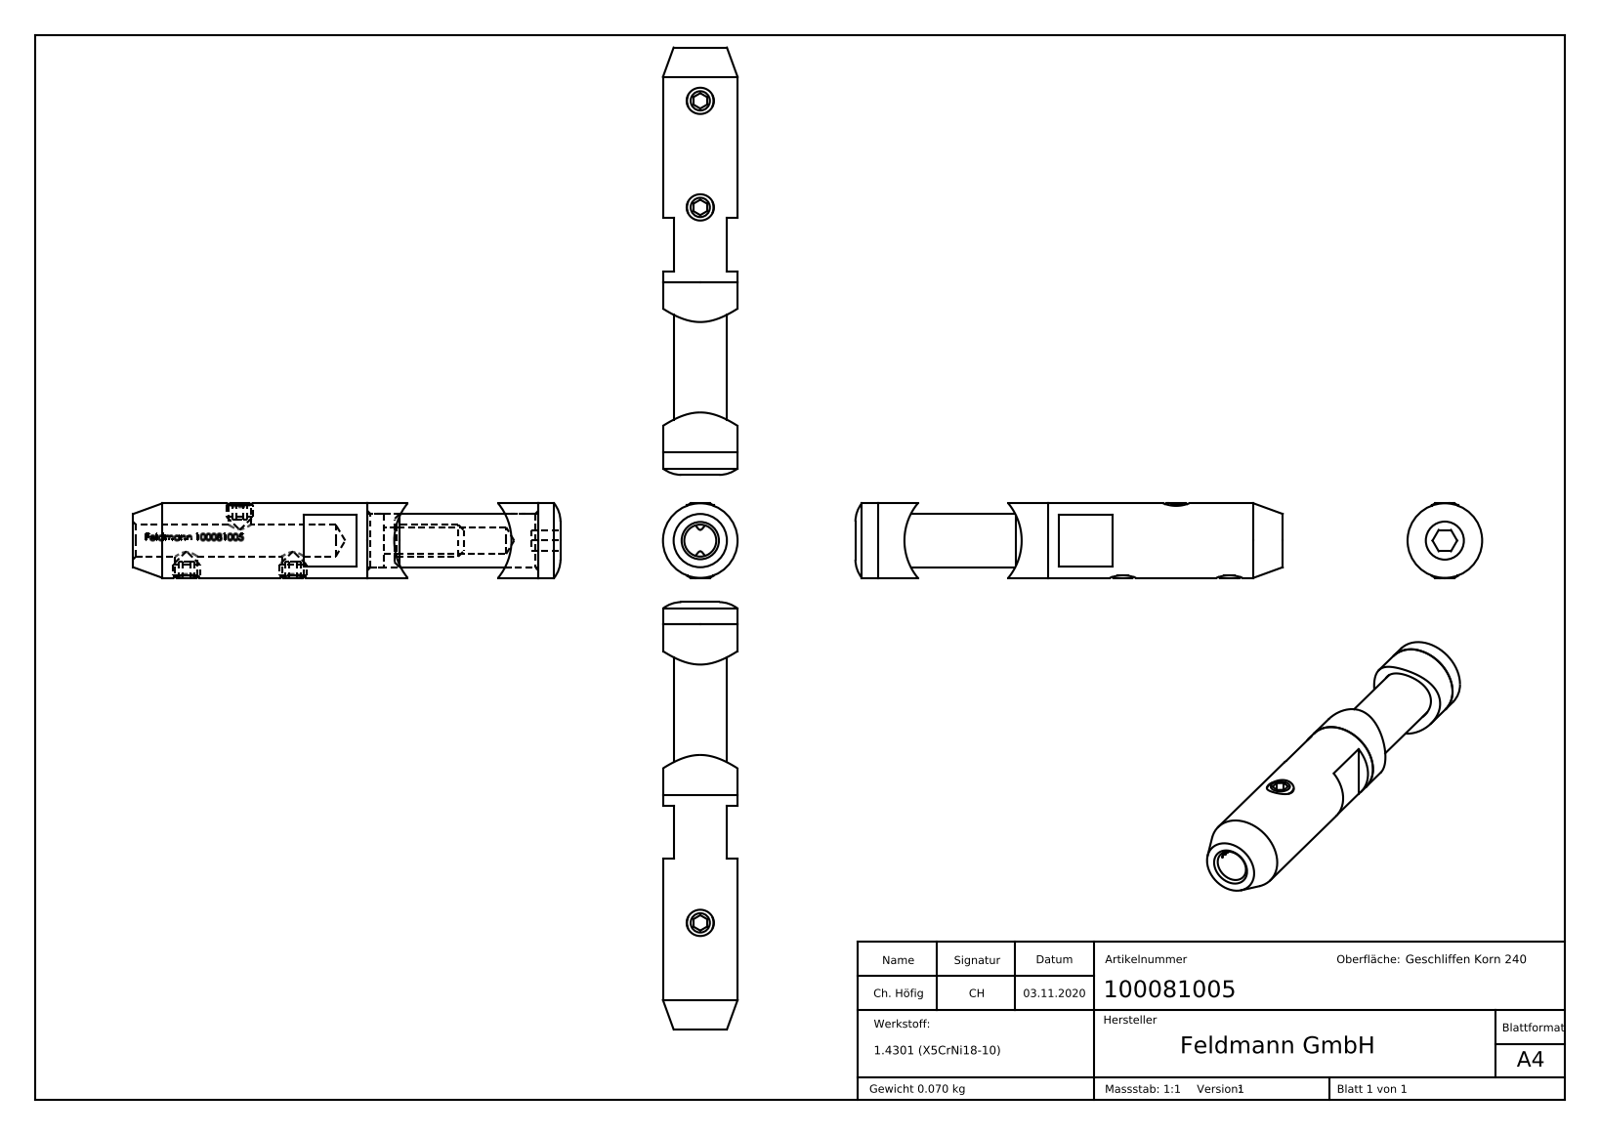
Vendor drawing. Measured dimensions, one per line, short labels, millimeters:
name: 10008100X Teil3; DIN 914 M5x6; DIN 914 M5x6_DIN914 M5x5; 100081005 (+5 more)
written by: SolidWorks 2018 (CONFIG_CONTROL_DESIGN)
unit: mm
bodies: 7 solids, 346 faces (119 planar, 71 cylindrical, 156 other)
size: 80.2 × 14 × 14
volume: 8 853 mm³; area: 6 552 mm²
holes: 3× ⌀4.2, 1× ⌀5, 1× ⌀6, 1× ⌀10.1
bosses: 3× ⌀5, 1× ⌀14, 1× ⌀10
rounds: 1× R3.1, 1× R11
face distances: 32, 10, 3, 44, 2, 5, 29, 2.5, 76, 47
hole spacings: 10, 20
